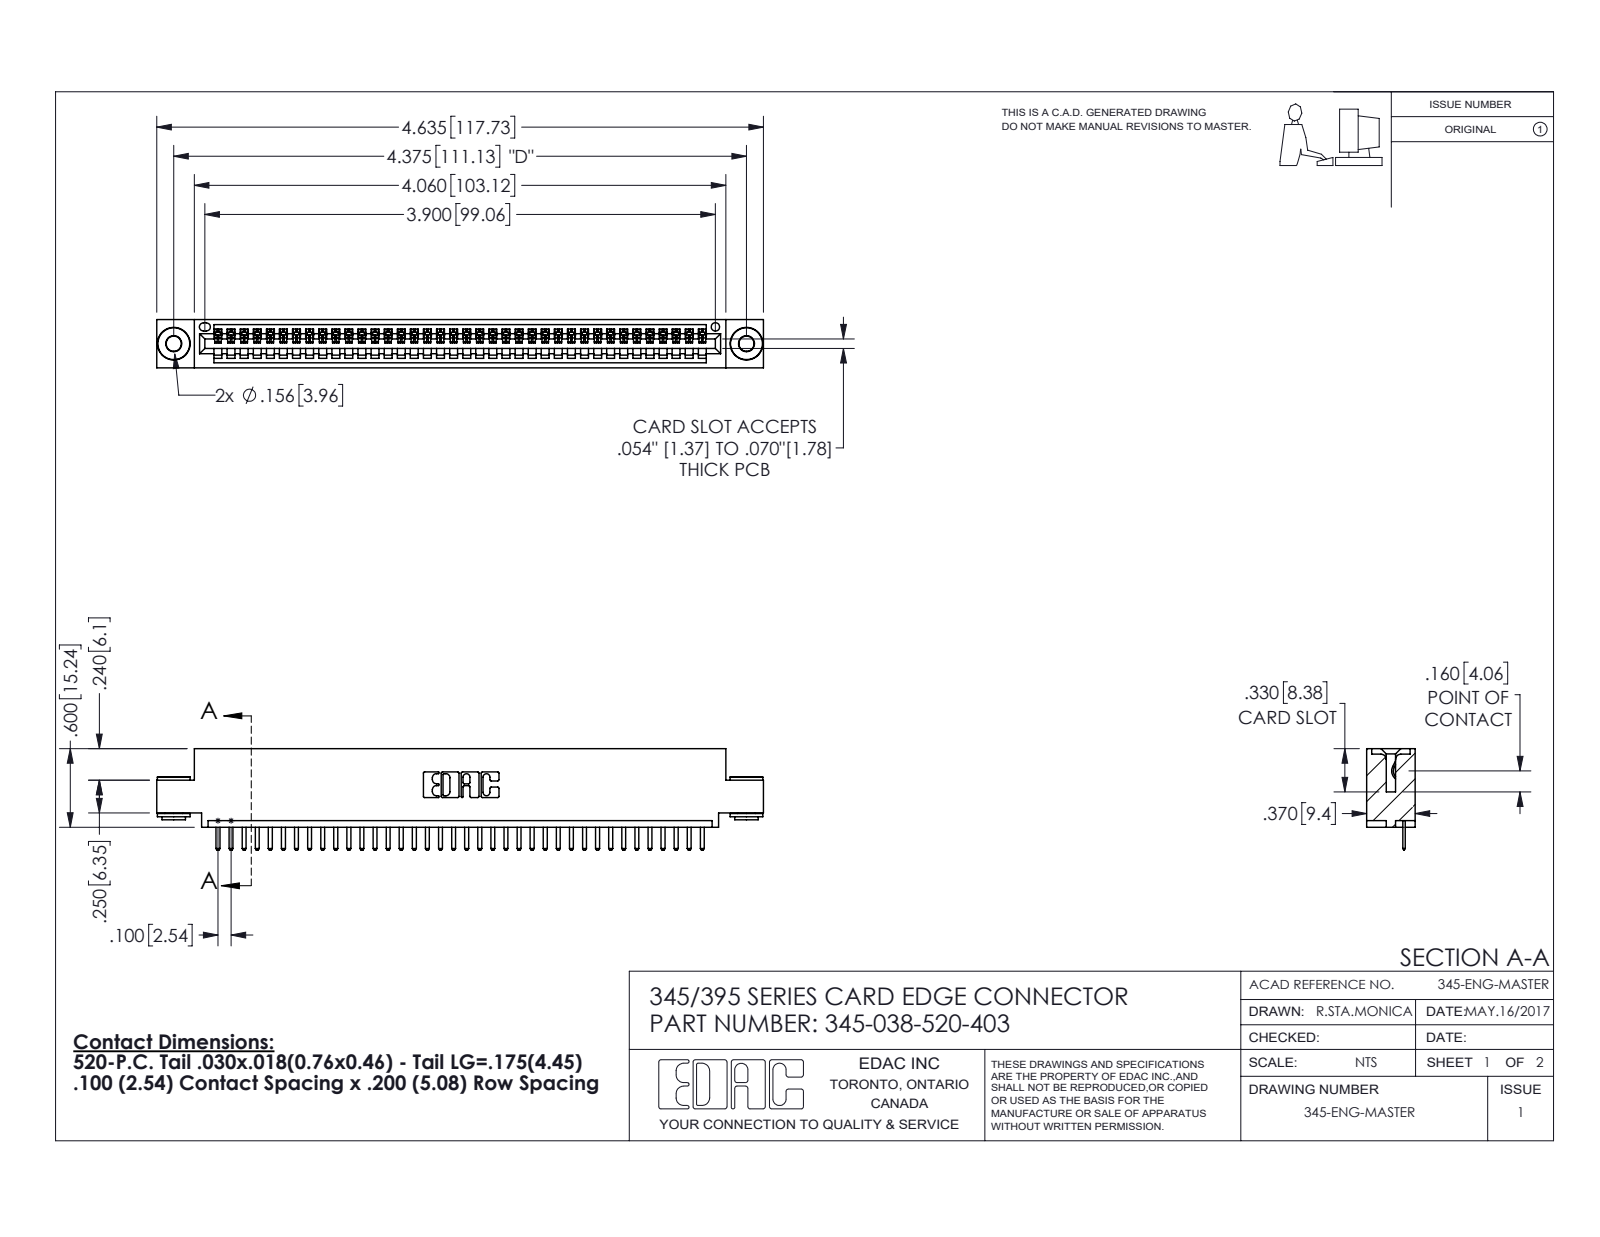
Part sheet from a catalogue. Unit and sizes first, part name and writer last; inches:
Units: inches
Overall size (bounding box): 4.635 × 0.775 × 0.37
Round holes (diameter × count): ⌀0.116 ×2, ⌀0.156 ×2, ⌀0.064 ×1
Round bosses / shafts (diameter × count): ⌀0.25 ×2, ⌀0.18 ×2, ⌀0.136 ×2
Partial cylindrical surfaces — rounded edges, fillets, slot ends (radius × count): R0.01 ×78, R0.006 ×76, R0.01 ×22, R0.007 ×6, R0.031 ×6, R0.026 ×3, R0.031 ×2, R0.04 ×2
Main face-to-face distances: 0.072, 0.298, 0.37, 0.2, 0.025, 0.098, 0.272, 0.225, 0.072, 0.149
Hole centre spacings: 0.27, 4.139, 4.375
Volume: 0.67 in³ · Surface area: 22.45 in²
Bodies: 41 solids, 2524 faces (1690 planar, 826 cylindrical, 8 other)
Part name (STEP PRODUCT): 345-250-002_345-250-002-102; 345-292-001_345-293-120; 345 Part_0.110 Offset - 0.156 Dia-TH; 345-038-520-403
STEP written by: SolidWorks 2016 (CONFIG_CONTROL_DESIGN)
